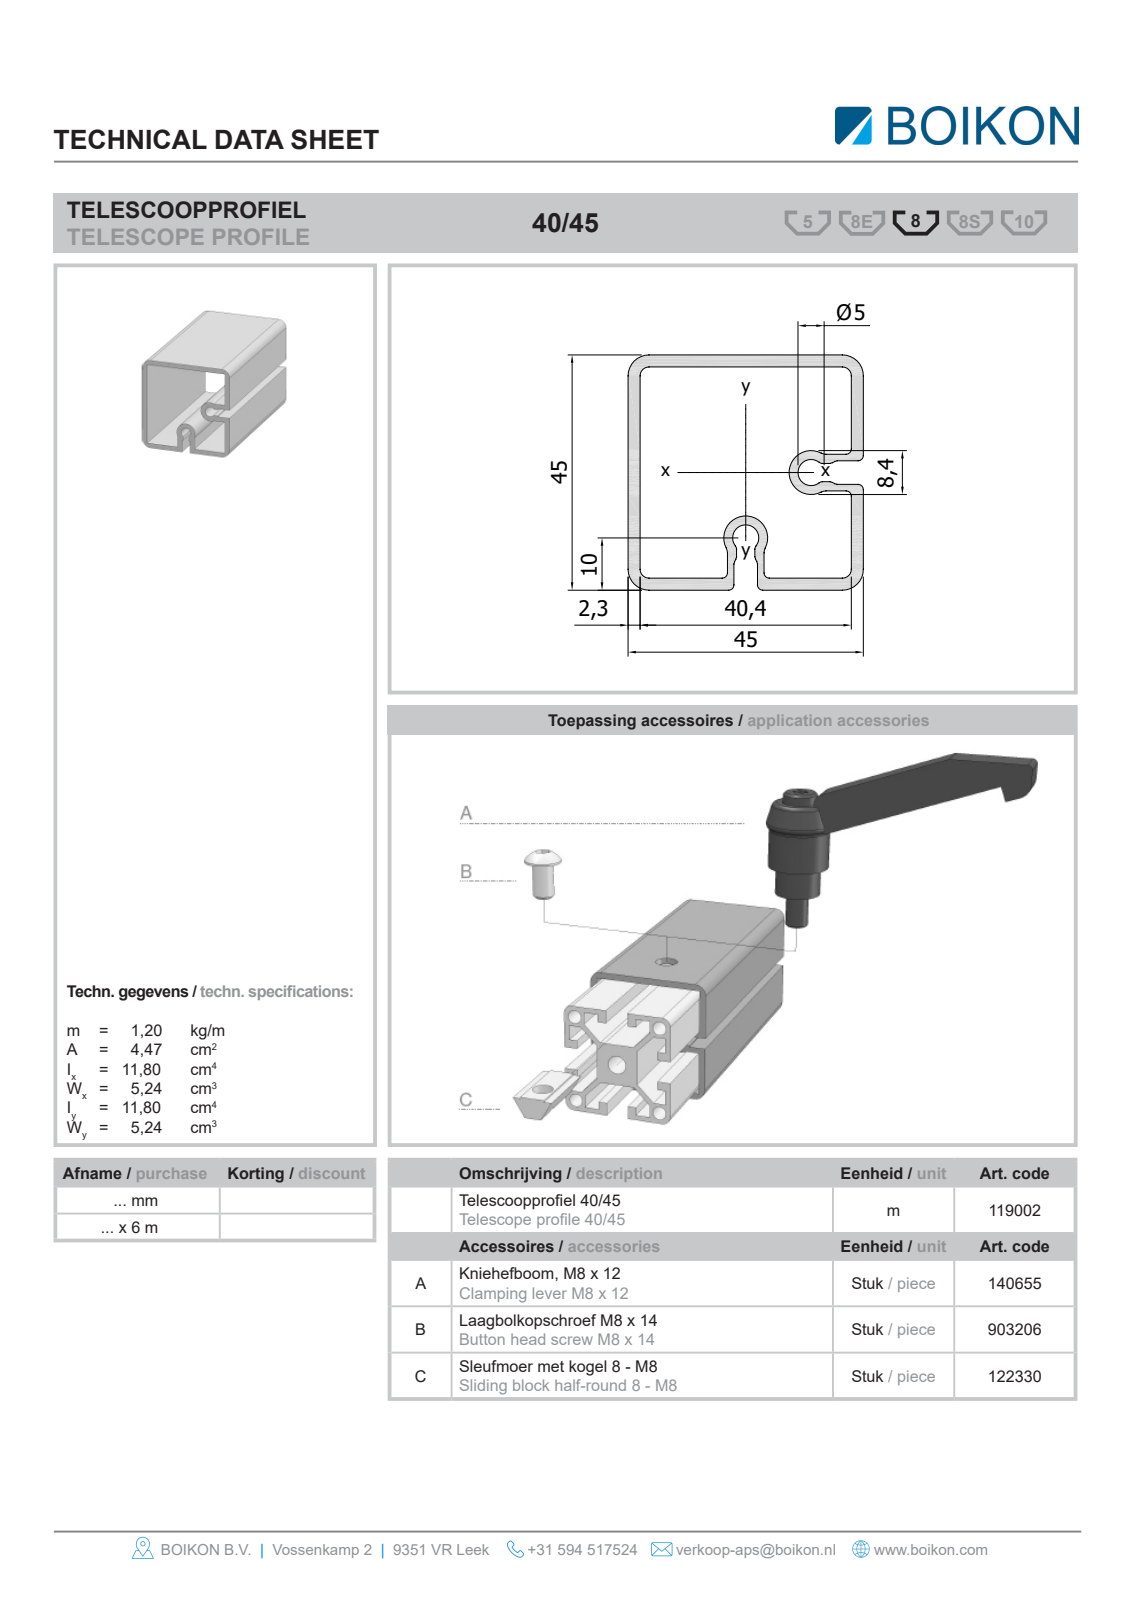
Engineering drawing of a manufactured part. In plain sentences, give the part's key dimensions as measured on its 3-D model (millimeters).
The part is named "Root; 119002Telescoopprofiel 40/45BOIKON0". Its 3-D file was written by "HiCAD 2013 1802.4 Build 509 (AUTOMOTIVE_DESIGN)". It is 1 solid with 38 faces: 30 planar, 8 cylindrical and 0 other. Overall it measures 1000 by 45 by 45 millimeters. Its volume is 488 543 cubic millimeters and its surface area 429 920 square millimeters. Partial cylindrical surfaces (rounded edges, fillets, slot ends): 4 of radius 4, 2 of radius 2.5, 2 of radius 4.8. The main face-to-face distances are 2.3, 42.7, 45, 40.4, 24.55, 18.15, 20.45, 22.25, 26.85, 15.85.
